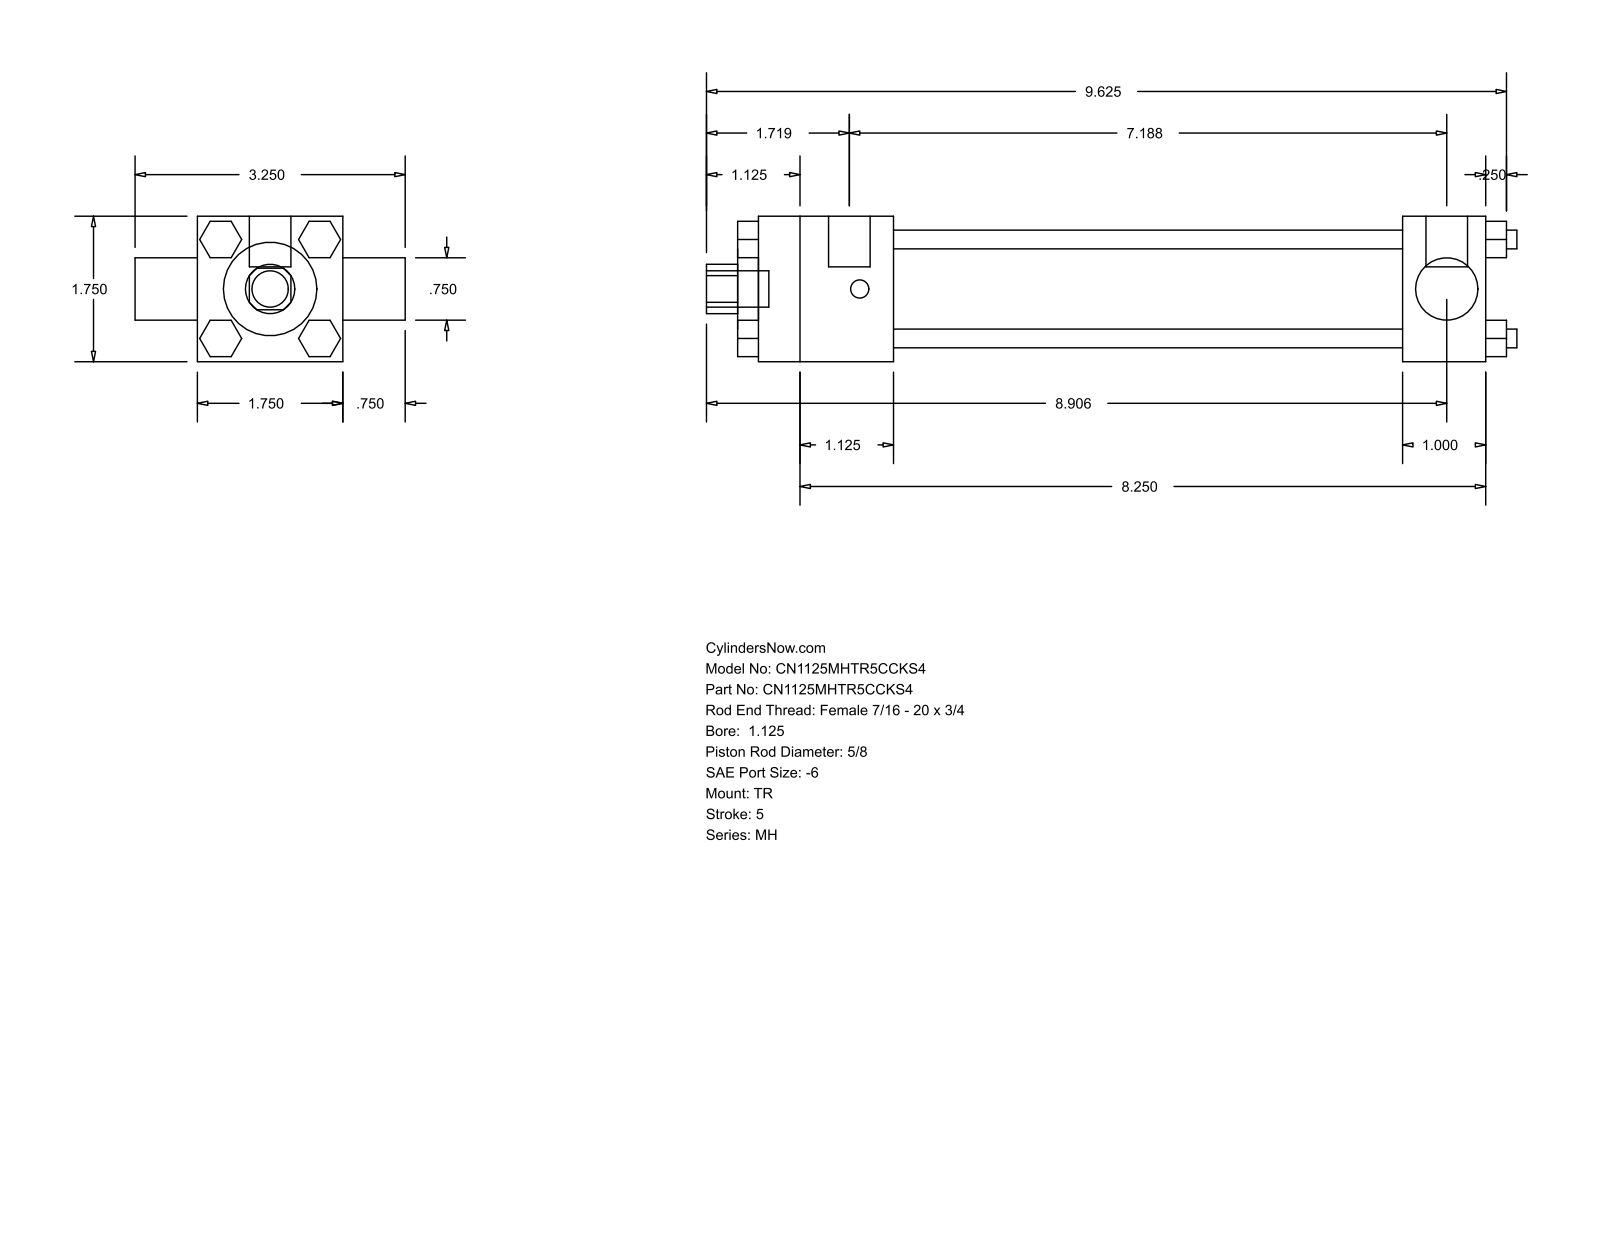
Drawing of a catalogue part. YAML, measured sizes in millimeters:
part_name: "MH_TR__0112_0.625"
step_written_by: "GSSL Pune (CONFIG_CONTROL_DESIGN)"
units: millimeters
bodies: {solids: 0, faces: 120, planar: 92, cylindrical: 28, other: 0}
overall_size: [247.65, 82.55, 44.45]
round_holes:
  - {diameter: 15.88, count: 1}
  - {diameter: 19.05, count: 1}
  - {diameter: 28.57, count: 1}
  - {diameter: 34.92, count: 1}
round_bosses_or_shafts:
  - {diameter: 5.71, count: 4}
  - {diameter: 5.56, count: 3}
  - {diameter: 12.7, count: 2}
  - {diameter: 11.11, count: 1}
partial_cylinders:
  - {radius: 7.54, count: 1}
face_to_face_distances: [44.46, 6.35, 228.59, 11.11, 155.57, 180.97, 25.4, 41.27, 196.84, 222.24]
